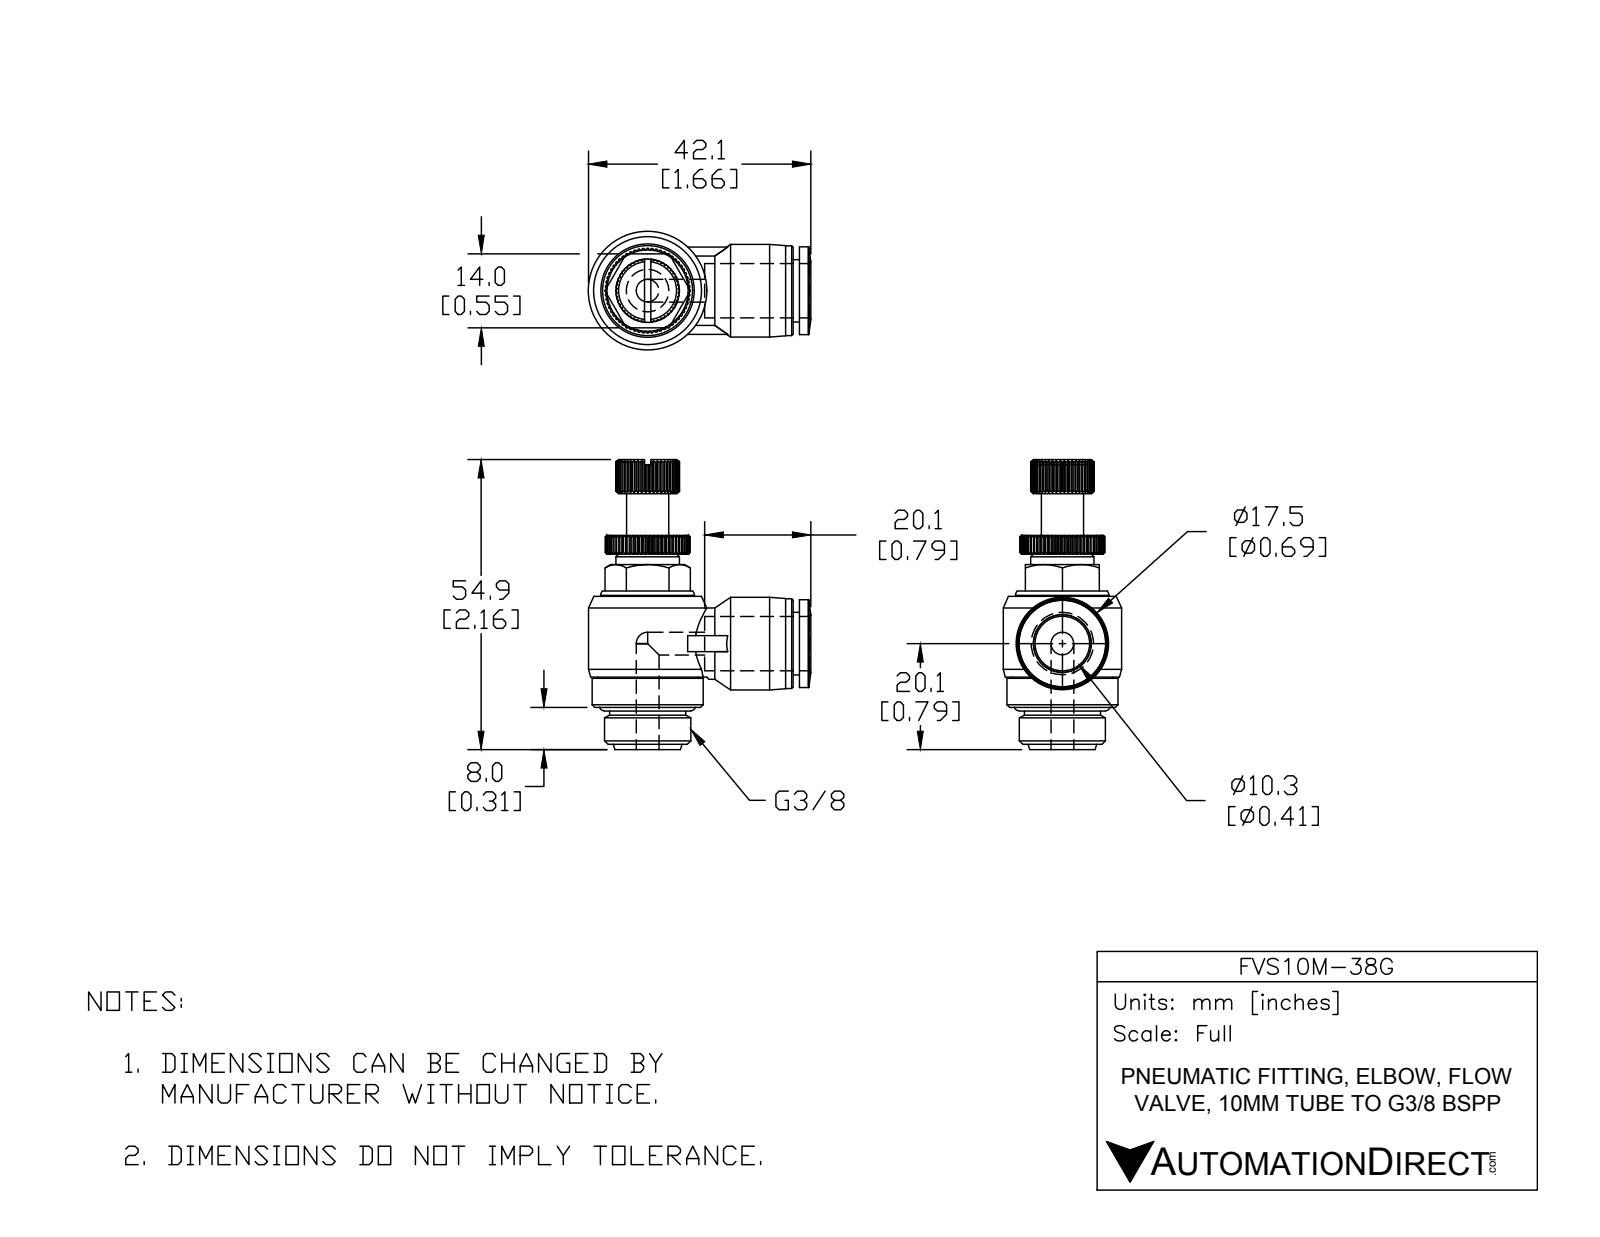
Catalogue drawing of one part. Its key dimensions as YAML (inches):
part_name: "FVS10M-38G"
step_written_by: "SolidWorks 2015 (AUTOMOTIVE_DESIGN)"
units: inches
bodies: {solids: 2, faces: 571, planar: 252, cylindrical: 143, other: 176}
overall_size: [2.161, 1.657, 0.882]
volume: 0.896
surface_area: 10.66
round_holes:
  - {diameter: 0.169, count: 2}
  - {diameter: 0.406, count: 1}
round_bosses_or_shafts:
  - {diameter: 0.882, count: 1}
  - {diameter: 0.827, count: 1}
  - {diameter: 0.748, count: 1}
  - {diameter: 0.689, count: 1}
  - {diameter: 0.675, count: 1}
  - {diameter: 0.669, count: 1}
  - {diameter: 0.654, count: 1}
  - {diameter: 0.642, count: 1}
partial_cylinders:
  - {radius: 0.315, count: 1}
face_to_face_distances: [1.142, 0.705, 0.315, 0.551, 0.039, 1.594, 0.045, 1.063, 0.453, 0.276]
